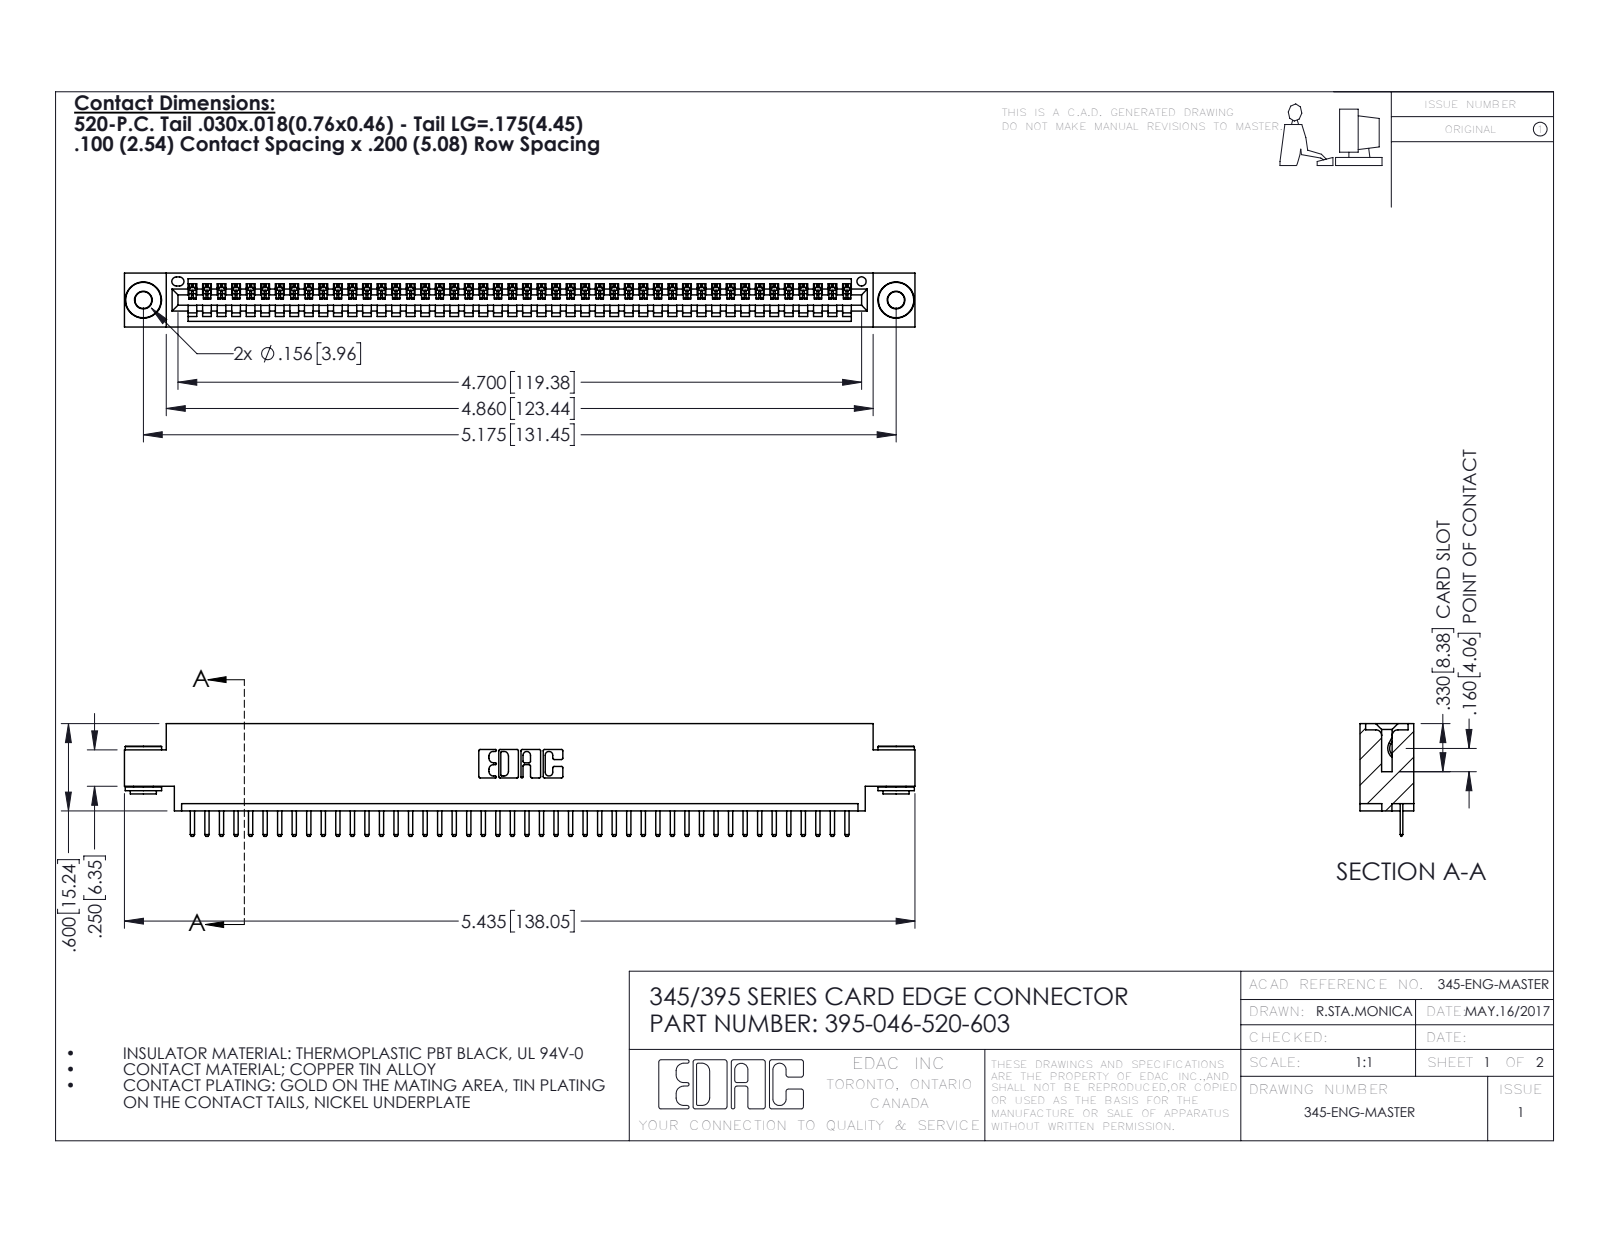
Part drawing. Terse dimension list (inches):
name: 395-046-520-603; 345-250-002_345-250-002-102; 345-292-001_345-293-120; 345 Part_0.170 Offset - 0.156 Dia-TH
written by: SolidWorks 2016 (CONFIG_CONTROL_DESIGN)
unit: in
bodies: 49 solids, 3020 faces (2026 planar, 986 cylindrical, 8 other)
size: 5.435 × 0.775 × 0.37
volume: 0.788 in³; area: 26.55 in²
holes: 2× ⌀0.116, 2× ⌀0.156, 1× ⌀0.064
bosses: 2× ⌀0.25, 2× ⌀0.18, 2× ⌀0.136
rounds: 94× R0.01, 92× R0.006, 22× R0.01, 6× R0.007, 6× R0.031, 3× R0.026, 2× R0.031, 2× R0.04
face distances: 0.072, 0.298, 0.37, 0.2, 0.098, 0.272, 0.025, 0.225, 0.072, 0.175
hole spacings: 0.27, 4.939, 5.175
